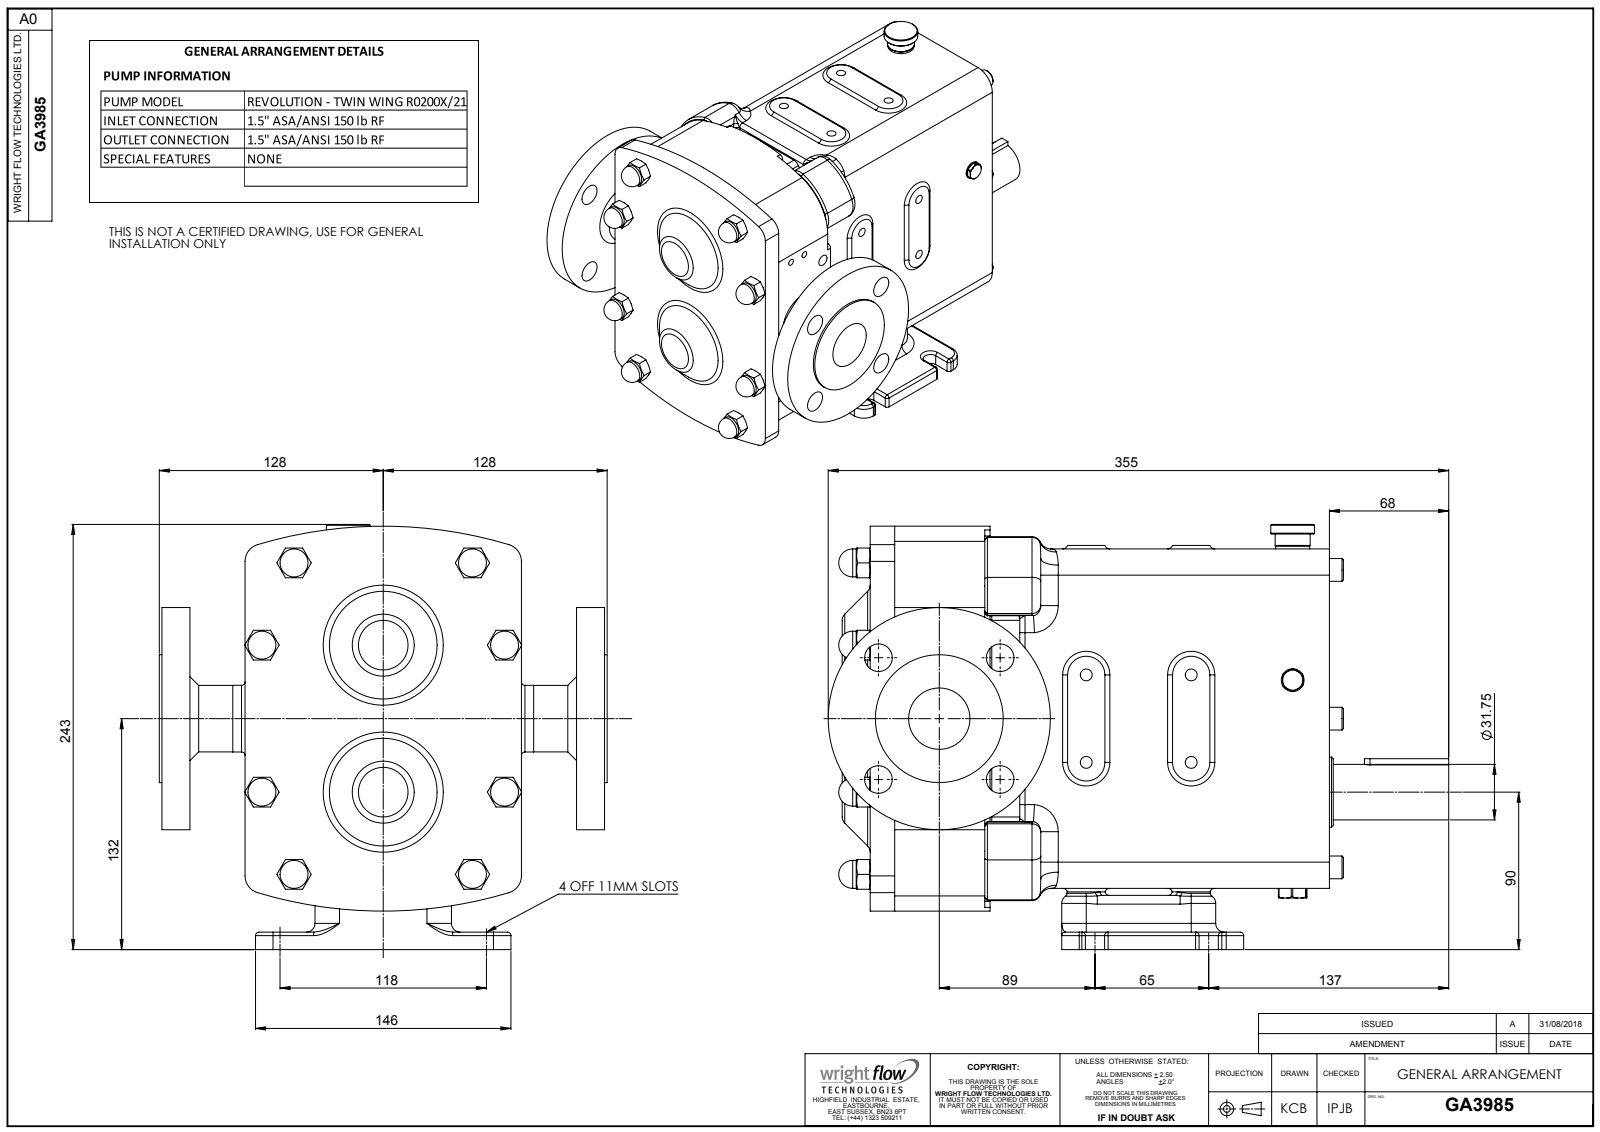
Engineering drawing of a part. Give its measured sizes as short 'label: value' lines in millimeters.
name: Copy of Z94-5301-22 - 1.5 INCH ASA 150^GA3985; GA3985; Copy of R0200 CPP H BSD^GA3985
written by: SolidWorks 2023 (AUTOMOTIVE_DESIGN)
unit: mm
bodies: 3 solids, 949 faces (297 planar, 316 cylindrical, 336 other)
size: 354.7 × 256 × 243
volume: 7 082 000 mm³; area: 422 793 mm²
holes: 8× ⌀6.8, 6× ⌀15.8, 4× ⌀5, 2× ⌀8.6, 1× ⌀23, 1× ⌀35.1
bosses: 8× ⌀16, 7× ⌀13, 2× ⌀38, 1× ⌀127, 1× ⌀73.1, 1× ⌀40, 1× ⌀38.1, 1× ⌀31.75
rounds: 30× R10, 28× R3, 24× R2, 19× R5, 8× R5.9, 8× R15, 4× R5.5, 4× R8
face distances: 194, 68.5, 24, 69.5, 55.5, 110, 165.5, 262.5, 16, 71.5
hole spacings: 50, 60, 78.1, 98.39, 49.19, 49.2, 14, 24.6
